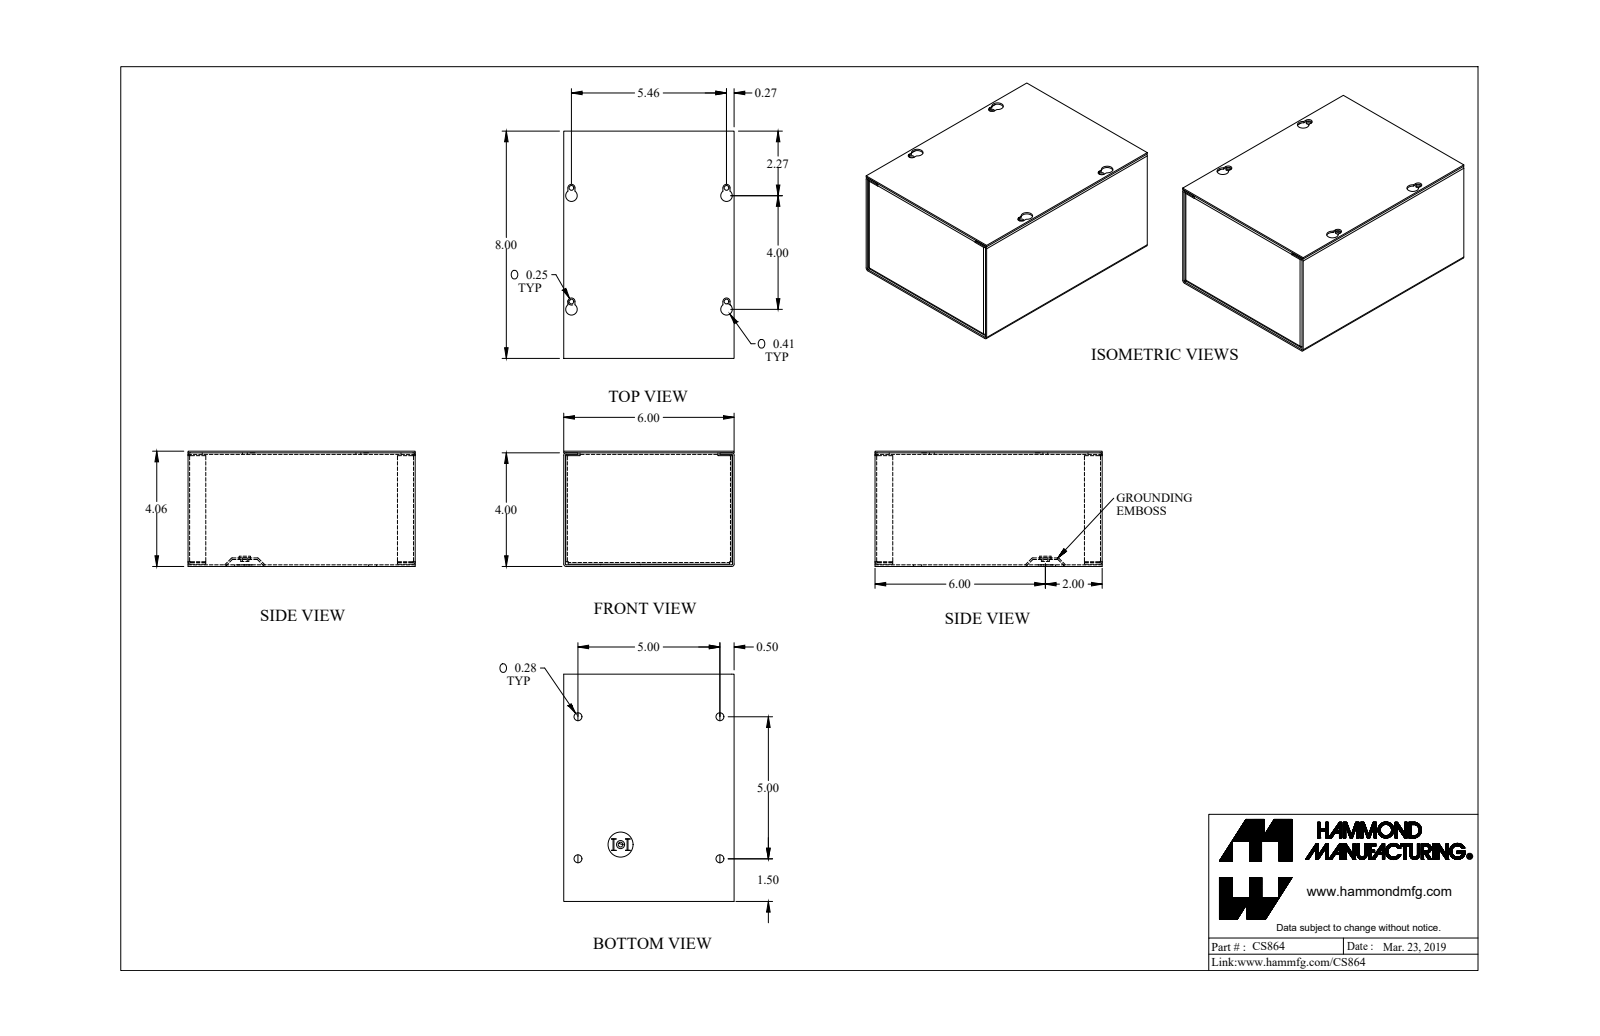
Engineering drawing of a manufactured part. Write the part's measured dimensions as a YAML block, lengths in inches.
part_name: "CS864_Default"
step_written_by: "SolidWorks 2019 (CONFIG_CONTROL_DESIGN)"
units: inches
bodies: {solids: 4, faces: 205, planar: 125, cylindrical: 72, other: 8}
overall_size: [8, 6, 4.057]
volume: 13.04
surface_area: 465.4
round_holes:
  - {diameter: 0.17, count: 5}
  - {diameter: 0.281, count: 4}
  - {diameter: 0.5, count: 1}
round_bosses_or_shafts:
  - {diameter: 0.492, count: 1}
  - {diameter: 0.284, count: 1}
partial_cylinders:
  - {radius: 0.029, count: 12}
  - {radius: 0.086, count: 12}
  - {radius: 0.057, count: 8}
  - {radius: 0.125, count: 4}
  - {radius: 0.203, count: 4}
face_to_face_distances: [0.057, 4, 5.943, 3.943, 4.057, 7.943, 6, 5.886, 8, 7.886]
hole_center_spacings: [0.55, 4.506, 5, 5.254, 6.9, 4, 5.46, 6.768]
